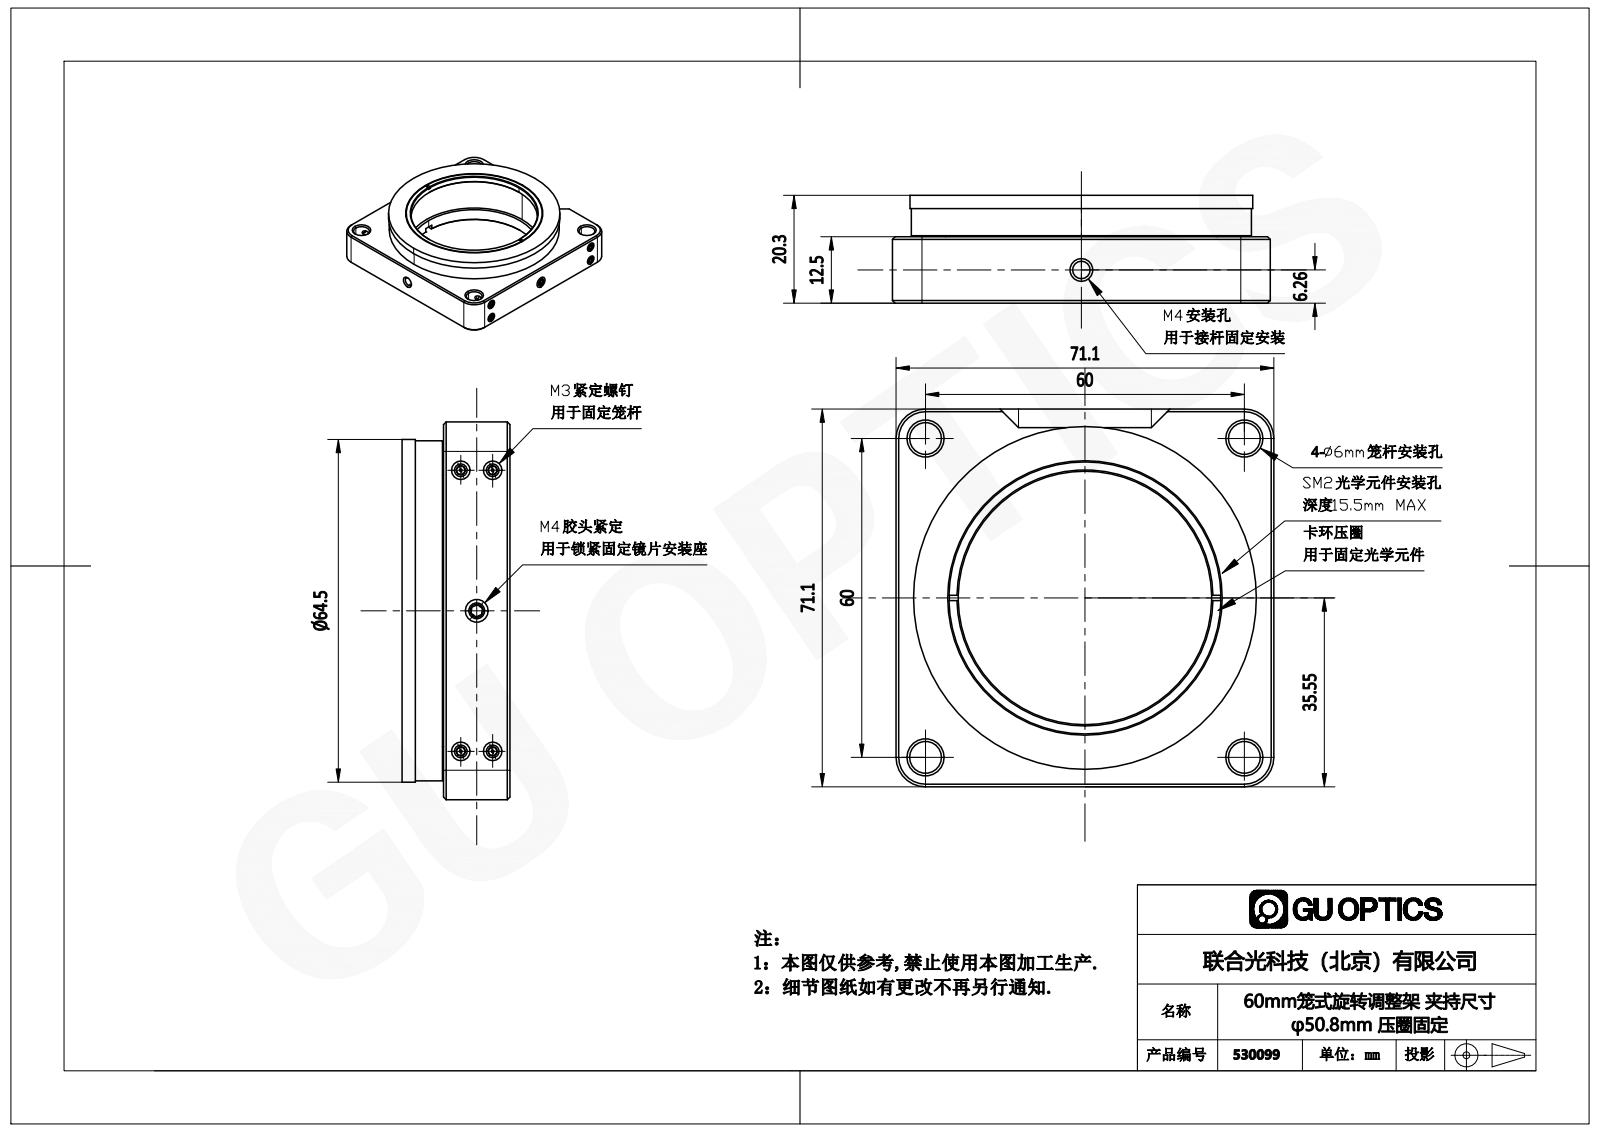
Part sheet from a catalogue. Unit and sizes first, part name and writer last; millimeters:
Units: millimetres
Overall size (bounding box): 71.1 × 71.1 × 20.3
Round holes (diameter × count): ⌀2.5 ×4, ⌀6 ×4, ⌀3.3 ×1, ⌀47.69 ×1, ⌀48.5 ×1, ⌀51.05 ×1, ⌀62 ×1
Round bosses / shafts (diameter × count): ⌀64.5 ×1, ⌀64 ×1, ⌀61.5 ×1
Partial cylindrical surfaces — rounded edges, fillets, slot ends (radius × count): R5.55 ×4, R1.6 ×2
Main face-to-face distances: 12.5, 20.3, 7.8, 71.1, 12.4, 20.2, 2.3, 2.2, 10.2, 18
Hole centre spacings: 42.43, 60, 6, 52.9, 53.24, 84.85
Bodies: 0 solids, 320 faces (111 planar, 47 cylindrical, 162 other)
STEP written by: SolidWorks 2018 (AUTOMOTIVE_DESIGN)
